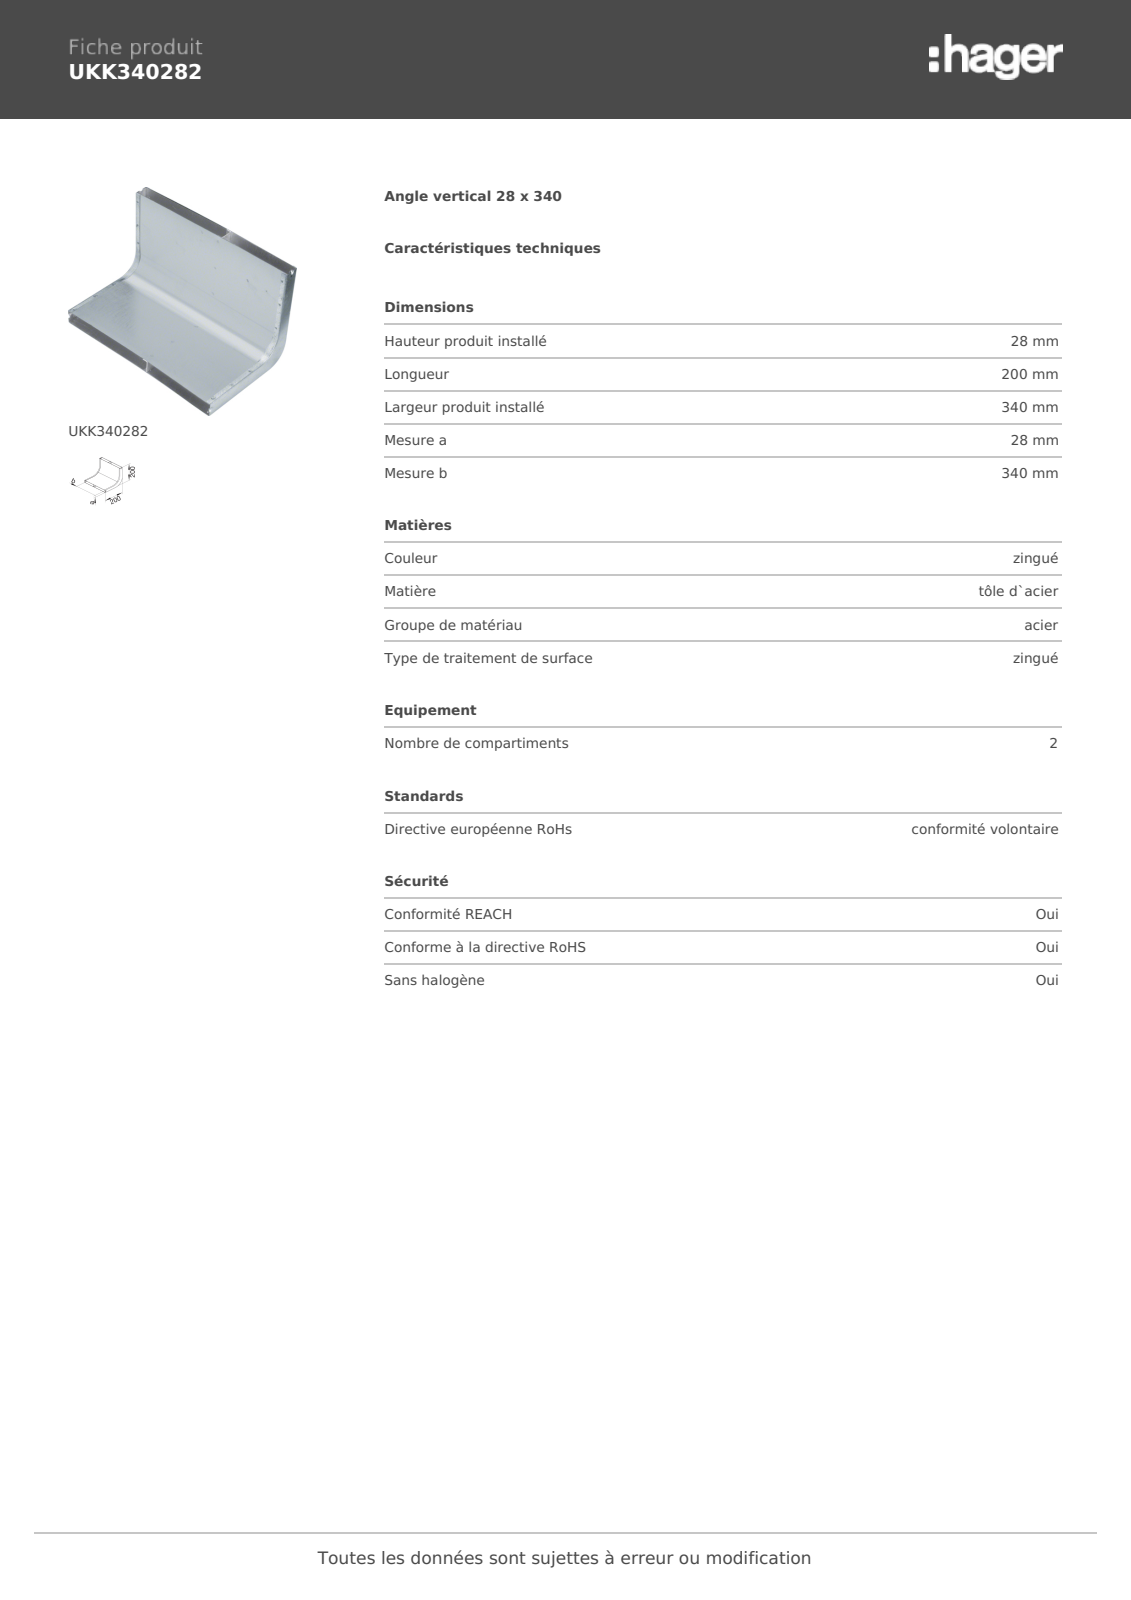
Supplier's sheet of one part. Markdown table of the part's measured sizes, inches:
| quantity | value |
| --- | --- |
| part name | UKKS_28-SIMPLIFIED; UKKA_340-SIMPLIFIED; UKKT_28-SIMPLIFIED; UKKI_340-28-SIMPLIFIED (+1 more) |
| STEP written by | CREO PARAMETRIC BY PTC INC, 2022024 (AUTOMOTIVE_DESIGN) |
| units | inches |
| bodies | 5 solids, 62 faces (49 planar, 13 cylindrical, 0 other) |
| overall size | 13.386 × 7.895 × 7.894 |
| volume | 13.3 in³ |
| surface area | 906.9 in² |
| partial cylindrical surfaces (radius × count) | 0.039 × 5, 0.069 × 3, 0.01 × 1 |
| main face-to-face distances | 0.03, 1.014, 0.984, 1.043, 13.356, 7.815, 5.541, 13.386, 13.327, 7.844 |
